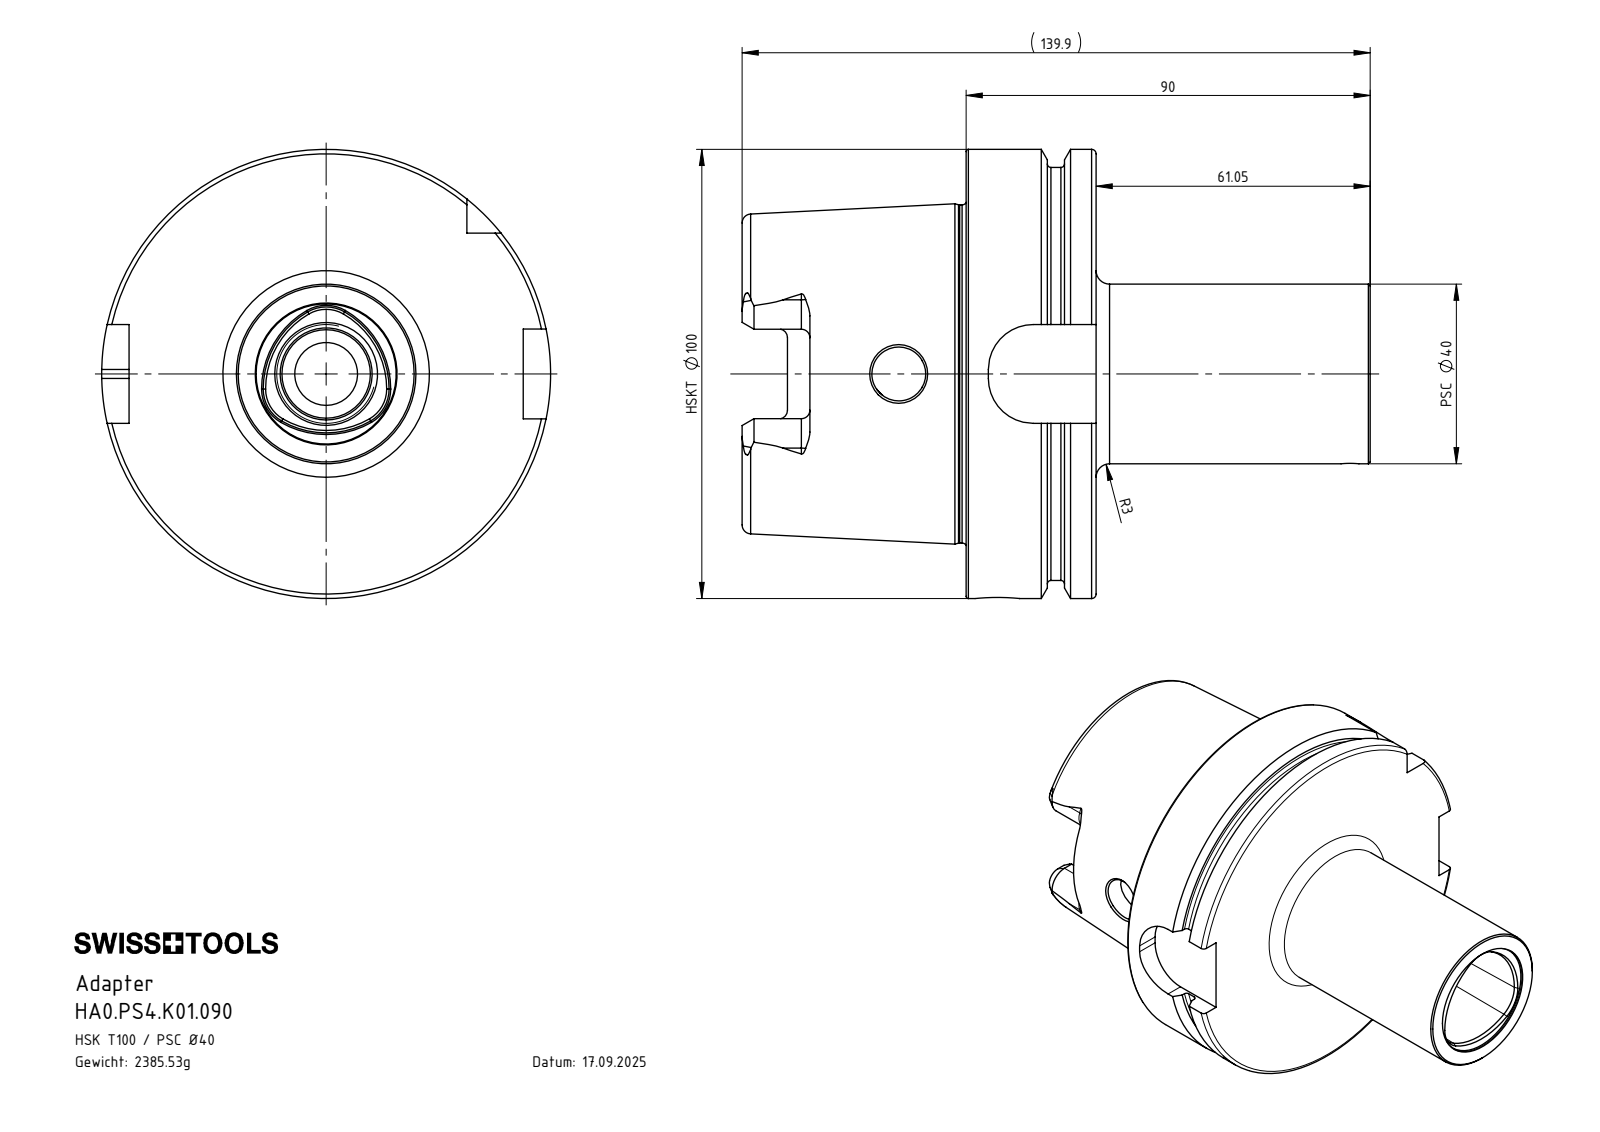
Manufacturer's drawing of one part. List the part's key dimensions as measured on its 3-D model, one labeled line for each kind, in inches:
Part name (STEP PRODUCT): PS4-ER1.K01.047_A_PreviewCfg; PS4-ER2.001.017_B; HA0-PS4.K01.090_A_Fertigbearbeitung; HA0.PS4.K01.090
STEP written by: SolidWorks 2022 (AUTOMOTIVE_DESIGN)
Units: inches
Bodies: 3 solids, 196 faces (69 planar, 49 cylindrical, 78 other)
Overall size (bounding box): 5.587 × 3.937 × 3.937
Volume: 19.24 in³ · Surface area: 104.7 in²
Round holes (diameter × count): ⌀0.157 ×3, ⌀0.394 ×1, ⌀0.472 ×1, ⌀0.551 ×1, ⌀0.567 ×1, ⌀0.807 ×1, ⌀0.886 ×1, ⌀1.024 ×1, ⌀1.244 ×1, ⌀2.087 ×1, ⌀2.48 ×1
Round bosses / shafts (diameter × count): ⌀3.937 ×1, ⌀3.62 ×1, ⌀2.963 ×1, ⌀1.575 ×1, ⌀0.921 ×1, ⌀0.866 ×1, ⌀0.772 ×1, ⌀0.744 ×1
Partial cylindrical surfaces — rounded edges, fillets, slot ends (radius × count): R0.075 ×6, R0.192 ×4, R0.394 ×4, R0.313 ×3, R0.771 ×3
Main face-to-face distances: 1.14, 0.49, 0.65, 1.965, 2.455, 3.104, 1.114, 2.429, 1.378, 3.457
Hole centre spacings: 3.091
